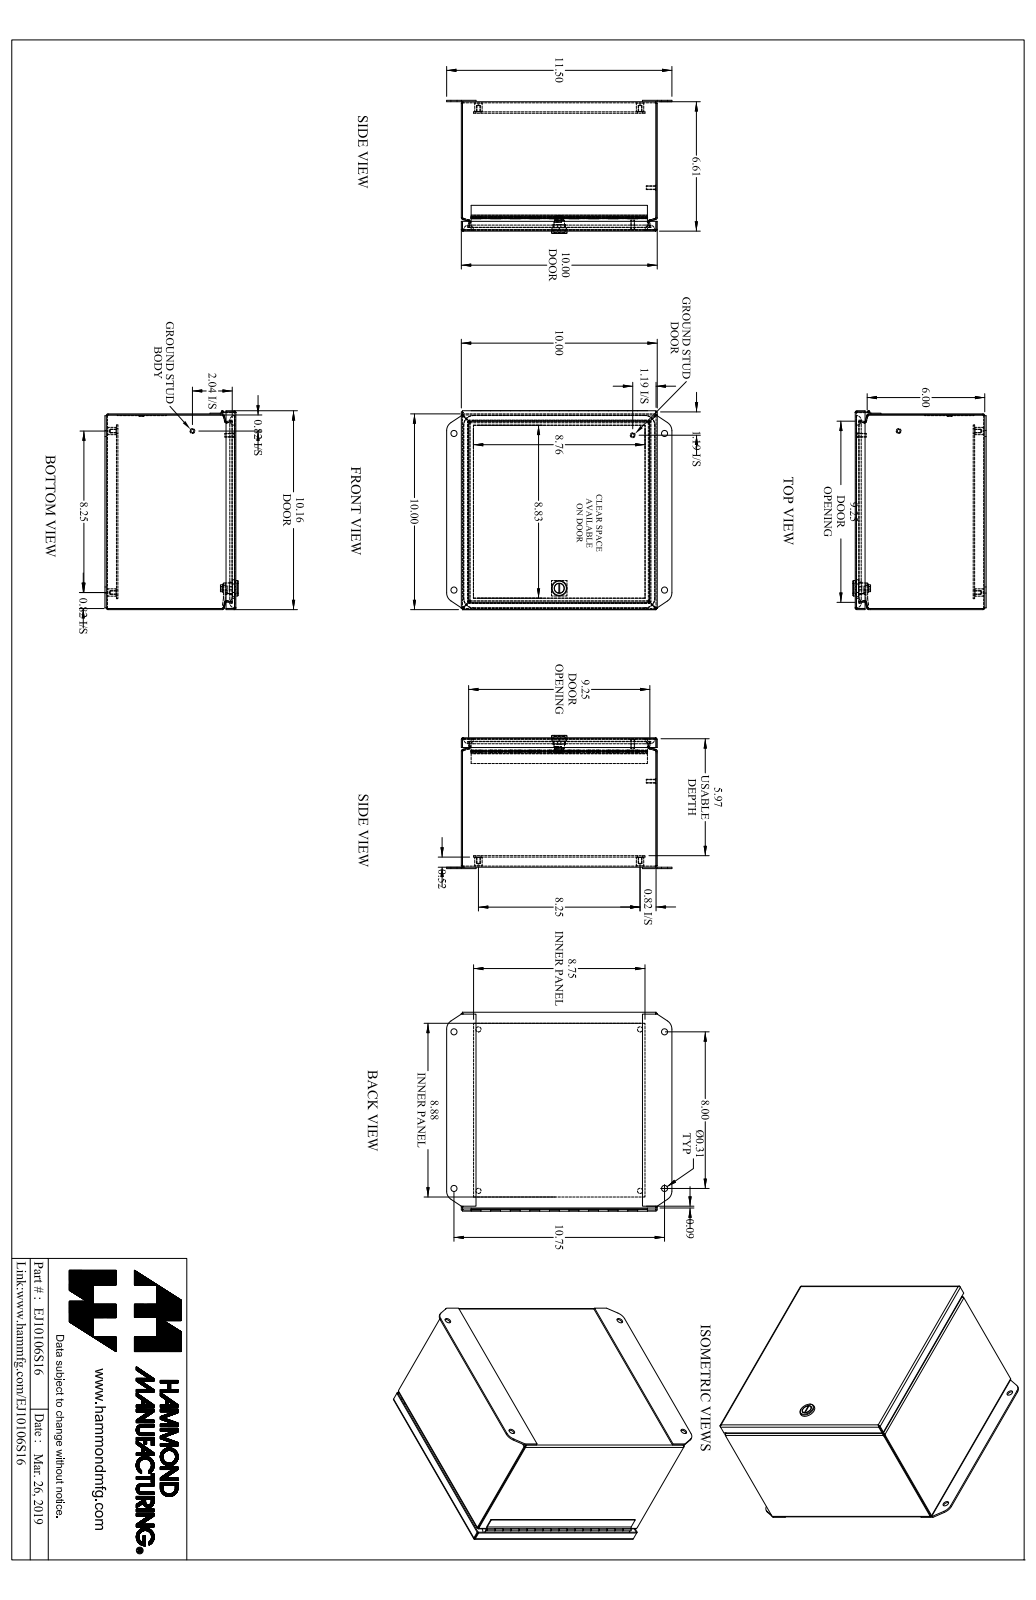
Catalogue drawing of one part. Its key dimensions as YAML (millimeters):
part_name: "EJ10106S16_Default"
step_written_by: "SolidWorks 2019 (CONFIG_CONTROL_DESIGN)"
units: millimeters
bodies: {solids: 16, faces: 596, planar: 310, cylindrical: 206, other: 80}
overall_size: [292.1, 258.2, 172.8]
volume: 645700
surface_area: 840600
round_holes:
  - {diameter: 4, count: 4}
  - {diameter: 6.7, count: 4}
  - {diameter: 8, count: 4}
  - {diameter: 1.3, count: 1}
  - {diameter: 13.1, count: 1}
round_bosses_or_shafts:
  - {diameter: 9.5, count: 4}
  - {diameter: 6.4, count: 2}
  - {diameter: 4.8, count: 2}
  - {diameter: 20, count: 1}
  - {diameter: 13.6, count: 1}
  - {diameter: 12.6, count: 1}
  - {diameter: 11, count: 1}
  - {diameter: 2.5, count: 1}
partial_cylinders:
  - {radius: 0.7, count: 16}
  - {radius: 2.2, count: 16}
  - {radius: 7.1, count: 12}
  - {radius: 6.4, count: 4}
  - {radius: 12.7, count: 4}
  - {radius: 12.7, count: 4}
  - {radius: 1.5, count: 2}
  - {radius: 0.8, count: 1}
face_to_face_distances: [1.4, 252.6, 166.5, 251.1, 254, 1.8, 15, 167.9, 165, 154.8]
hole_center_spacings: [209.6, 31.9, 241.3, 317.5, 208.8, 104.9, 136.6, 203.2]
